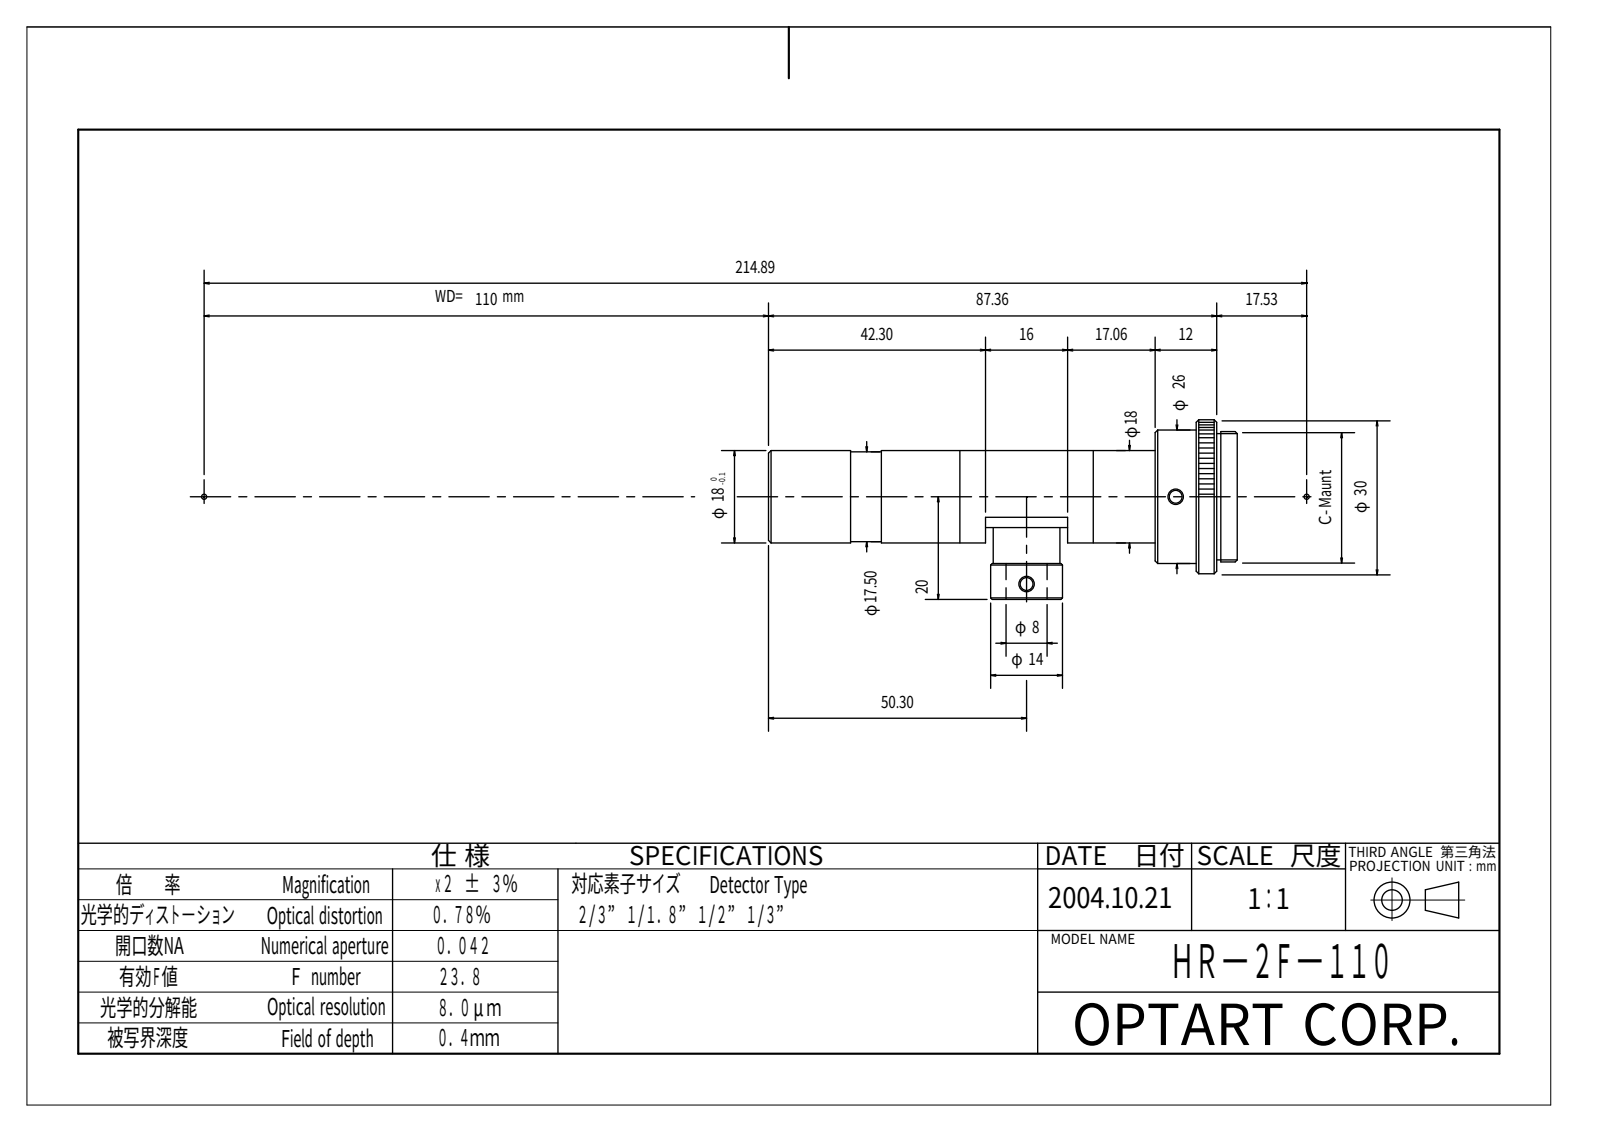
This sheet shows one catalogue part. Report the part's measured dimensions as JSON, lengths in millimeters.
{"part_name": "HR-2F-110 3D-Data", "step_written_by": "SolidWorks 2016 (AUTOMOTIVE_DESIGN)", "units": "millimeters", "bodies": {"solids": 1, "faces": 118, "planar": 28, "cylindrical": 46, "other": 44}, "overall_size": [91.66, 35, 30], "volume_mm3": 26947, "surface_area_mm2": 8790, "round_holes": [[6, 1], [8, 1], [13.5, 1], [14, 1], [14.5, 1], [15.5, 1]], "round_bosses_or_shafts": [[3, 4], [30, 1], [26, 1], [25.4, 1], [24.6, 1], [18, 1], [17.5, 1], [14, 1]], "partial_cylinders_radius": [[10, 1]], "face_to_face_distances": [6, 4, 16, 8, 12, 10, 2, 14, 33.36, 5]}
